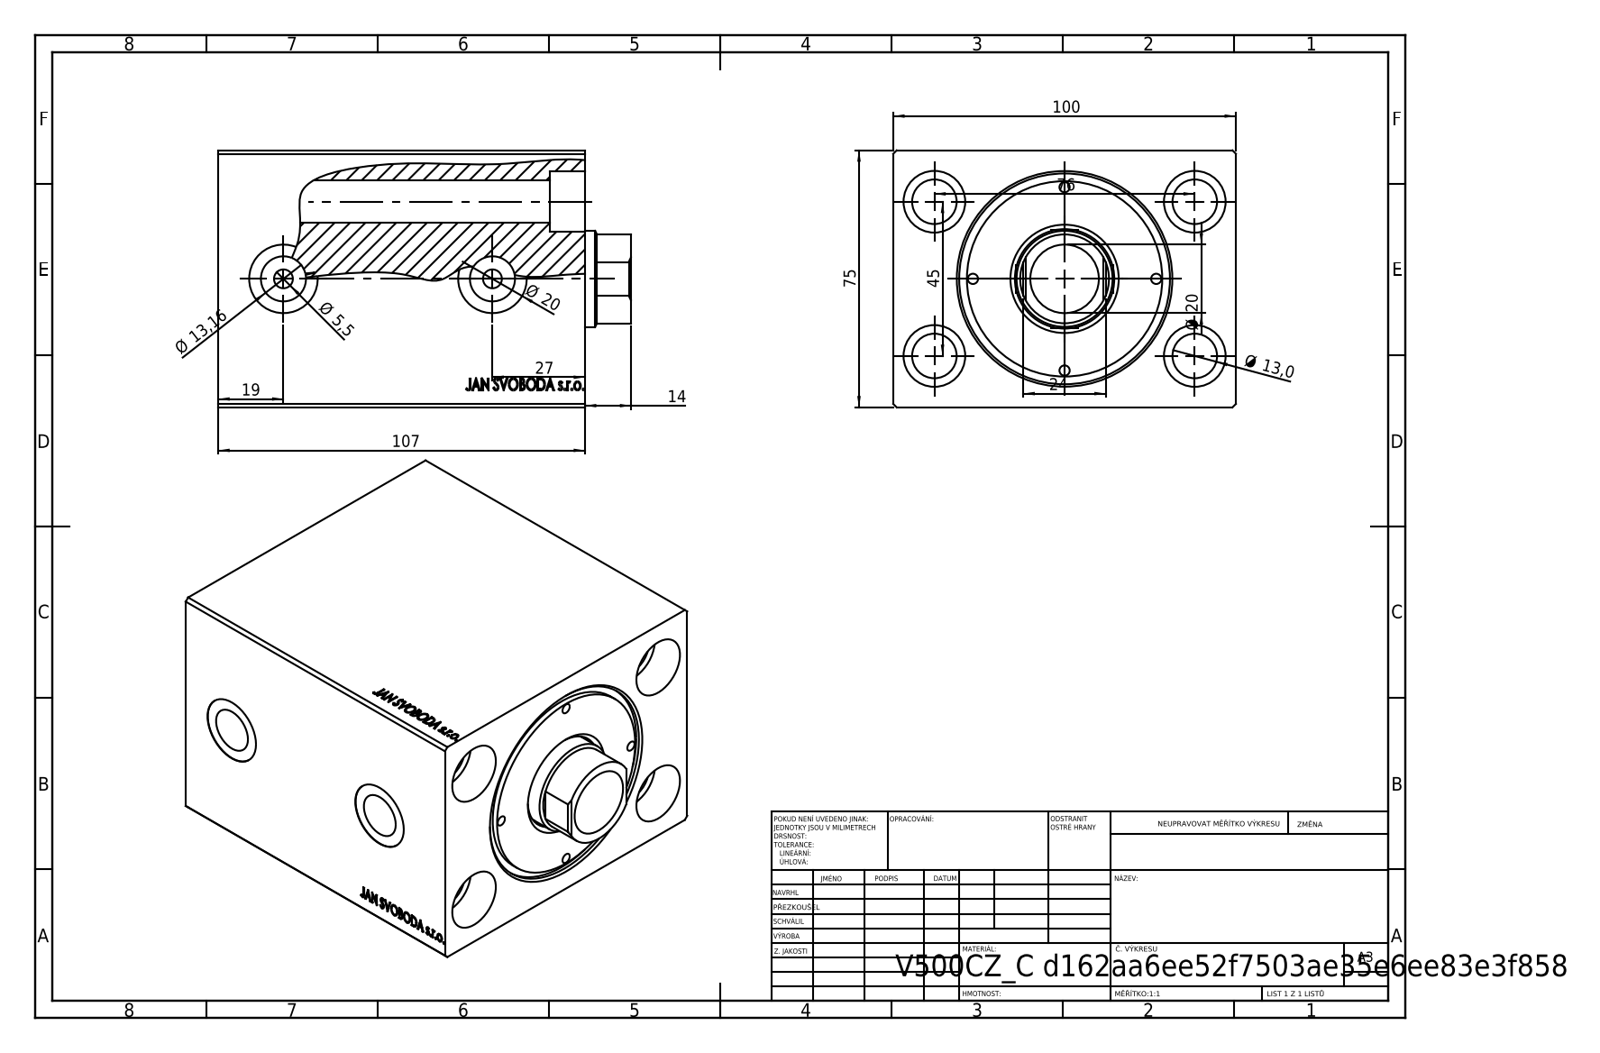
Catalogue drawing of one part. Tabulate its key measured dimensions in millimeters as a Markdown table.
| quantity | value |
| --- | --- |
| part name | V500CZ_C; V500CZ_VC_vysunovaci_C; V500CZ_VCP_C |
| STEP written by | SolidWorks 2019 (CONFIG_CONTROL_DESIGN) |
| units | millimeters |
| bodies | 3 solids, 888 faces (415 planar, 79 cylindrical, 394 other) |
| overall size | 120.5 × 100 × 75 |
| volume | 697 026 mm³ |
| surface area | 104 008 mm² |
| round holes (diameter × count) | 3 × 4, 13 × 4, 18 × 4, 20 × 3, 5.5 × 2, 13.16 × 2, 13.6 × 2, 28 × 1, 29 × 1, 36 × 1, 50 × 1, 61.5 × 1 |
| round bosses / shafts (diameter × count) | 57 × 1 |
| partial cylindrical surfaces (radius × count) | 12.96 × 1 |
| main face-to-face distances | 75, 100, 107, 60, 47, 11.8, 25, 48.2, 95.2, 10 |
| hole center spacings | 25.16, 26.75, 37.83, 38.24, 44.16, 62.21, 68.55, 45 |
